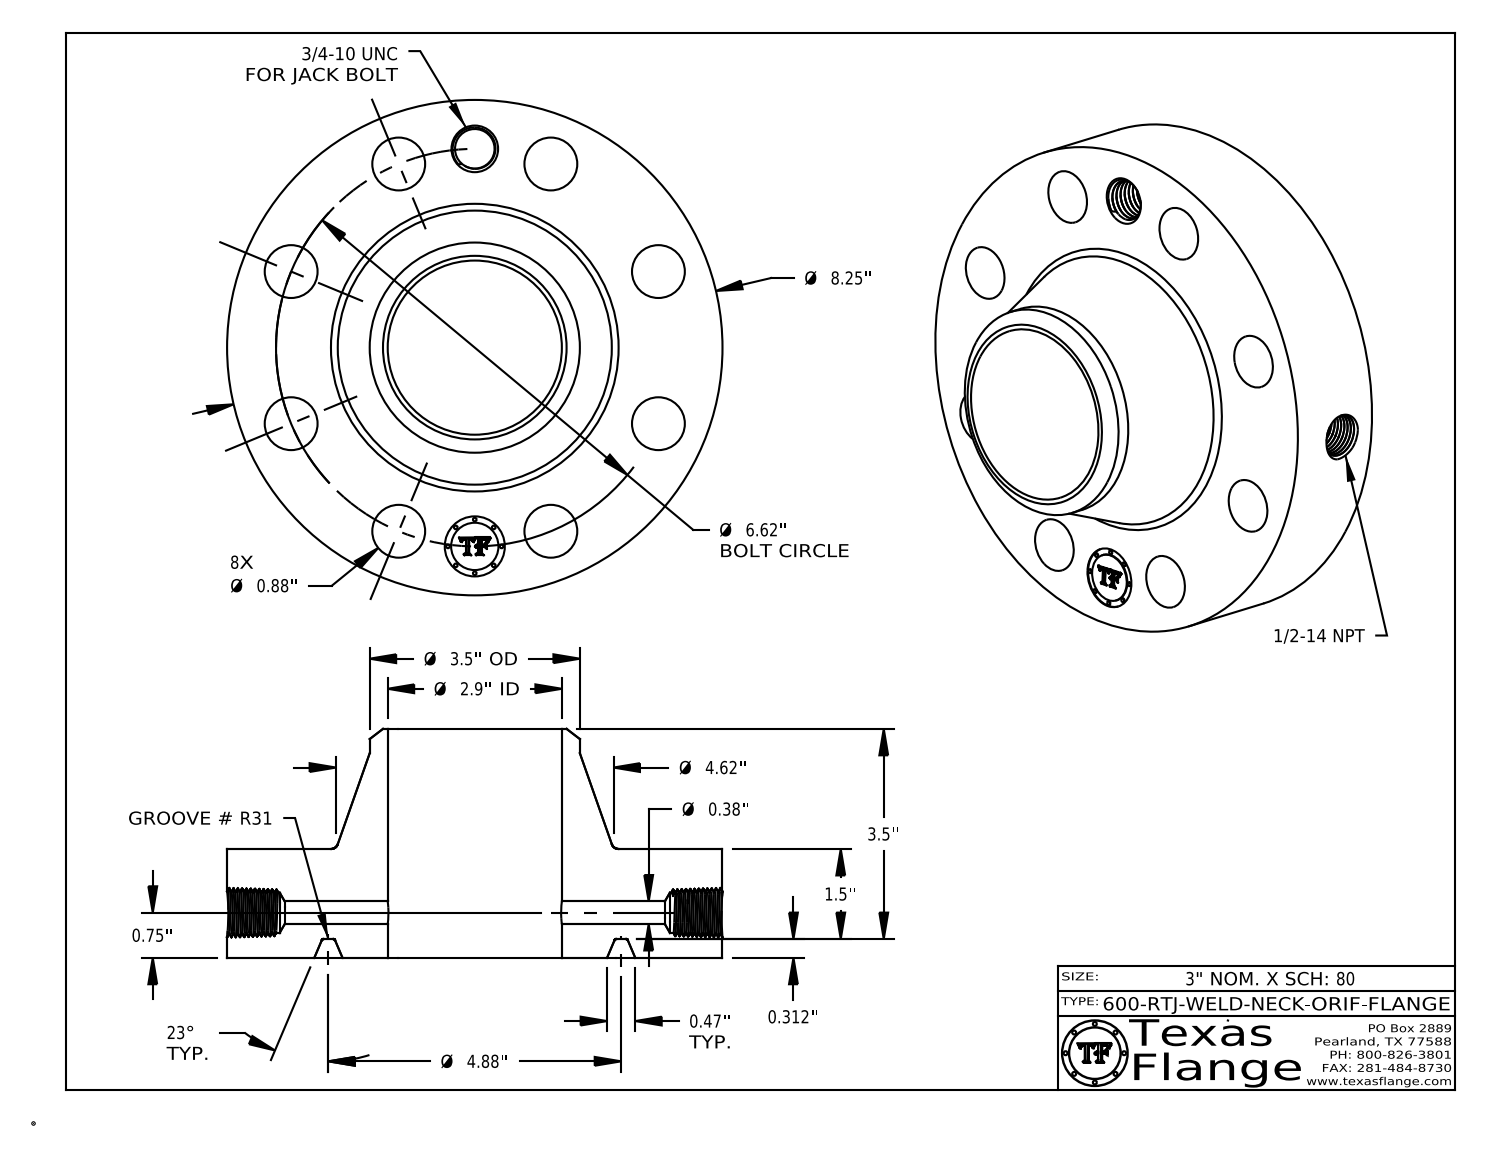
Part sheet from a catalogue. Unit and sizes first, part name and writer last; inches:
Units: inches
Overall size (bounding box): 8.25 × 8.25 × 3.812
Round holes (diameter × count): ⌀0.88 ×8, ⌀0.375 ×1, ⌀0.656 ×1, ⌀0.672 ×1, ⌀1 ×1, ⌀2.9 ×1
Round bosses / shafts (diameter × count): ⌀0.061 ×8, ⌀8.25 ×1, ⌀3.5 ×1, ⌀0.788 ×1
Main face-to-face distances: 1.812, 0.312, 1.5, 3.812, 3.5, 2, 0.015, 1.797, 1.485, 2.015
Hole centre spacings: 3.31, 4.681, 6.116, 6.62, 1.291, 2.533, 2.533, 3.678
Volume: 83.89 in³ · Surface area: 244.7 in²
Bodies: 1 solid, 795 faces (370 planar, 96 cylindrical, 329 other)
Part name (STEP PRODUCT): 600-RTJ-WELD-NECK
STEP written by: CATIA V5 STEP AP214 (AUTOMOTIVE_DESIGN)
